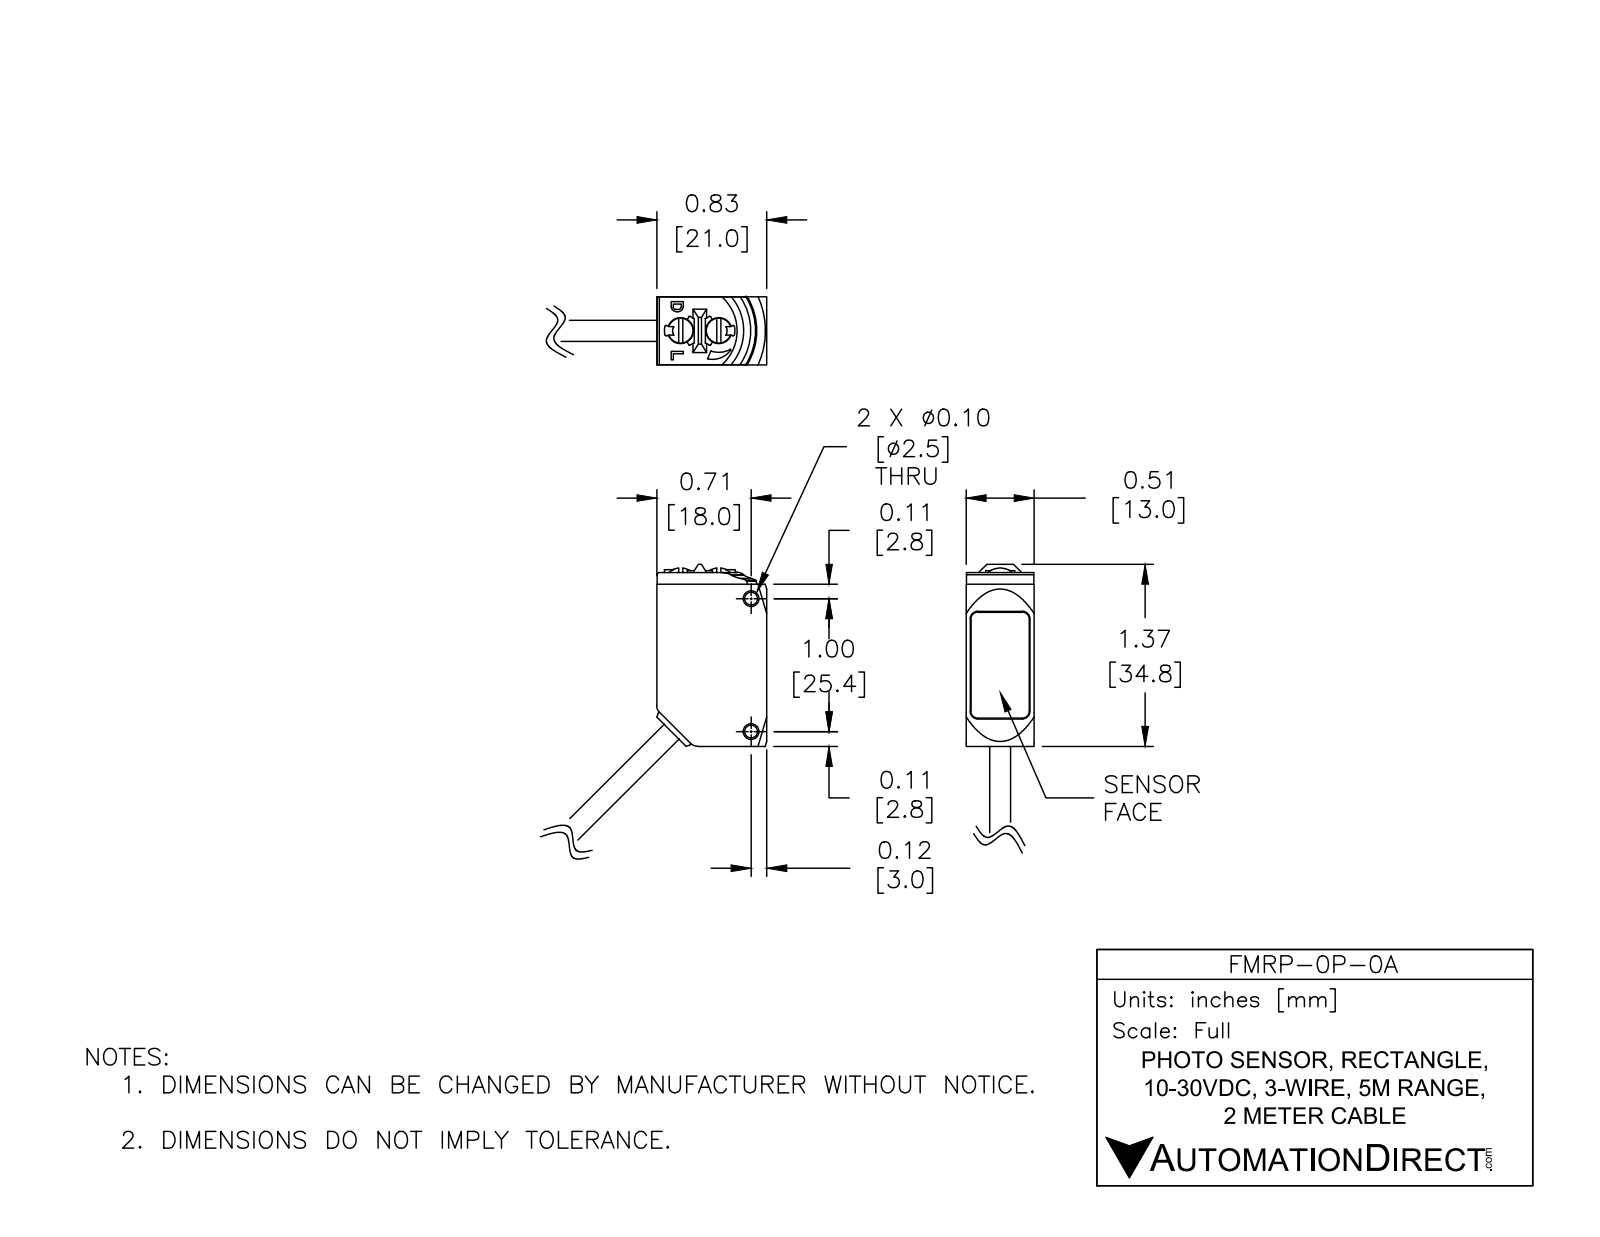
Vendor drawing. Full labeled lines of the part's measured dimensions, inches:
Part name (STEP PRODUCT): FMRP-0P-0A
STEP written by: SolidWorks 2017 (AUTOMOTIVE_DESIGN)
Units: inches
Bodies: 1 solid, 186 faces (89 planar, 72 cylindrical, 25 other)
Overall size (bounding box): 2.084 × 1.541 × 0.512
Volume: 0.542 in³ · Surface area: 5.476 in²
Round holes (diameter × count): ⌀0.097 ×2, ⌀0.197 ×2
Round bosses / shafts (diameter × count): ⌀0.189 ×2, ⌀0.157 ×1
Partial cylindrical surfaces — rounded edges, fillets, slot ends (radius × count): R0.018 ×7, R0.02 ×7, R0.008 ×4, R0.01 ×4, R0.051 ×4, R0.059 ×4, R0.004 ×3, R0.018 ×2
Main face-to-face distances: 0.512, 0.827, 1.307, 0.035, 0.51, 0.031, 0.48, 0.037, 0.474, 0.472
Hole centre spacings: 0.287, 1
